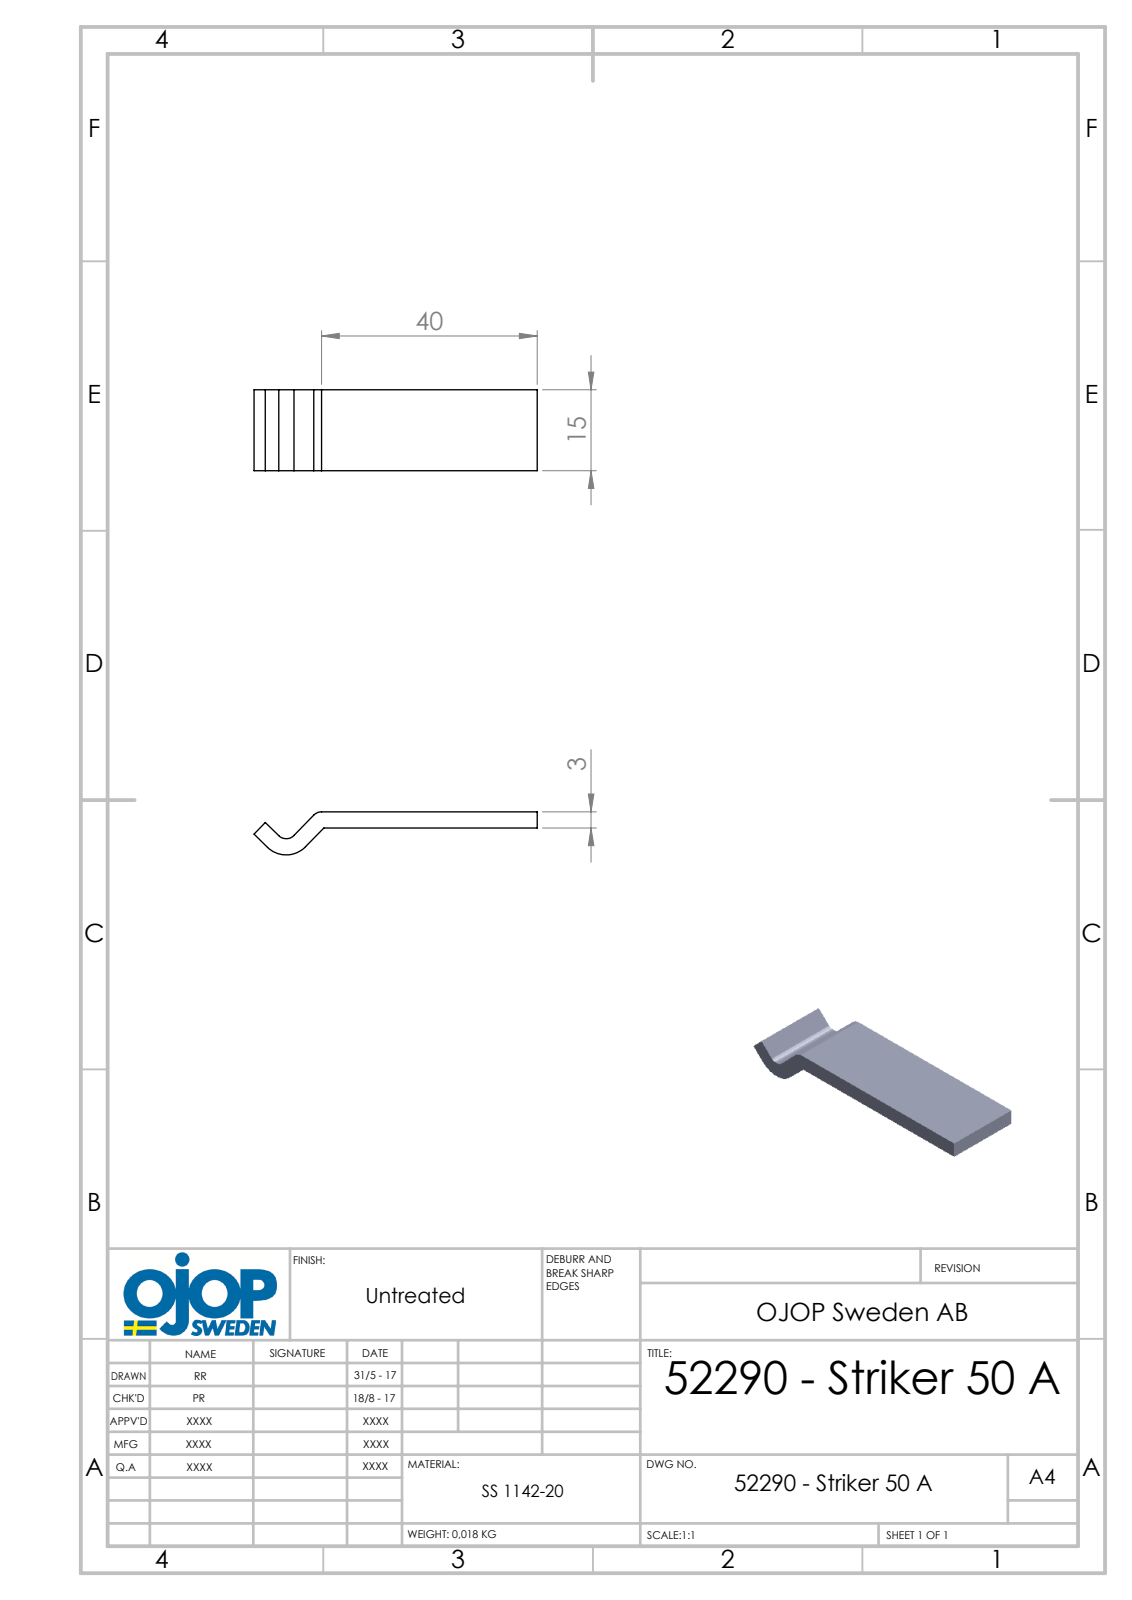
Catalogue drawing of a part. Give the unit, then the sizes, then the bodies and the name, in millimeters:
Units: millimetres
Overall size (bounding box): 52.53 × 15 × 8
Partial cylindrical surfaces — rounded edges, fillets, slot ends (radius × count): R2 ×2, R5 ×1
Main face-to-face distances: 3, 15, 5.5, 8.5
Volume: 2 460 mm³ · Surface area: 2 057 mm²
Bodies: 1 solid, 13 faces (10 planar, 3 cylindrical, 0 other)
Part name (STEP PRODUCT): 52290 - Striker 50 A
STEP written by: SolidWorks 2015 (AUTOMOTIVE_DESIGN)
